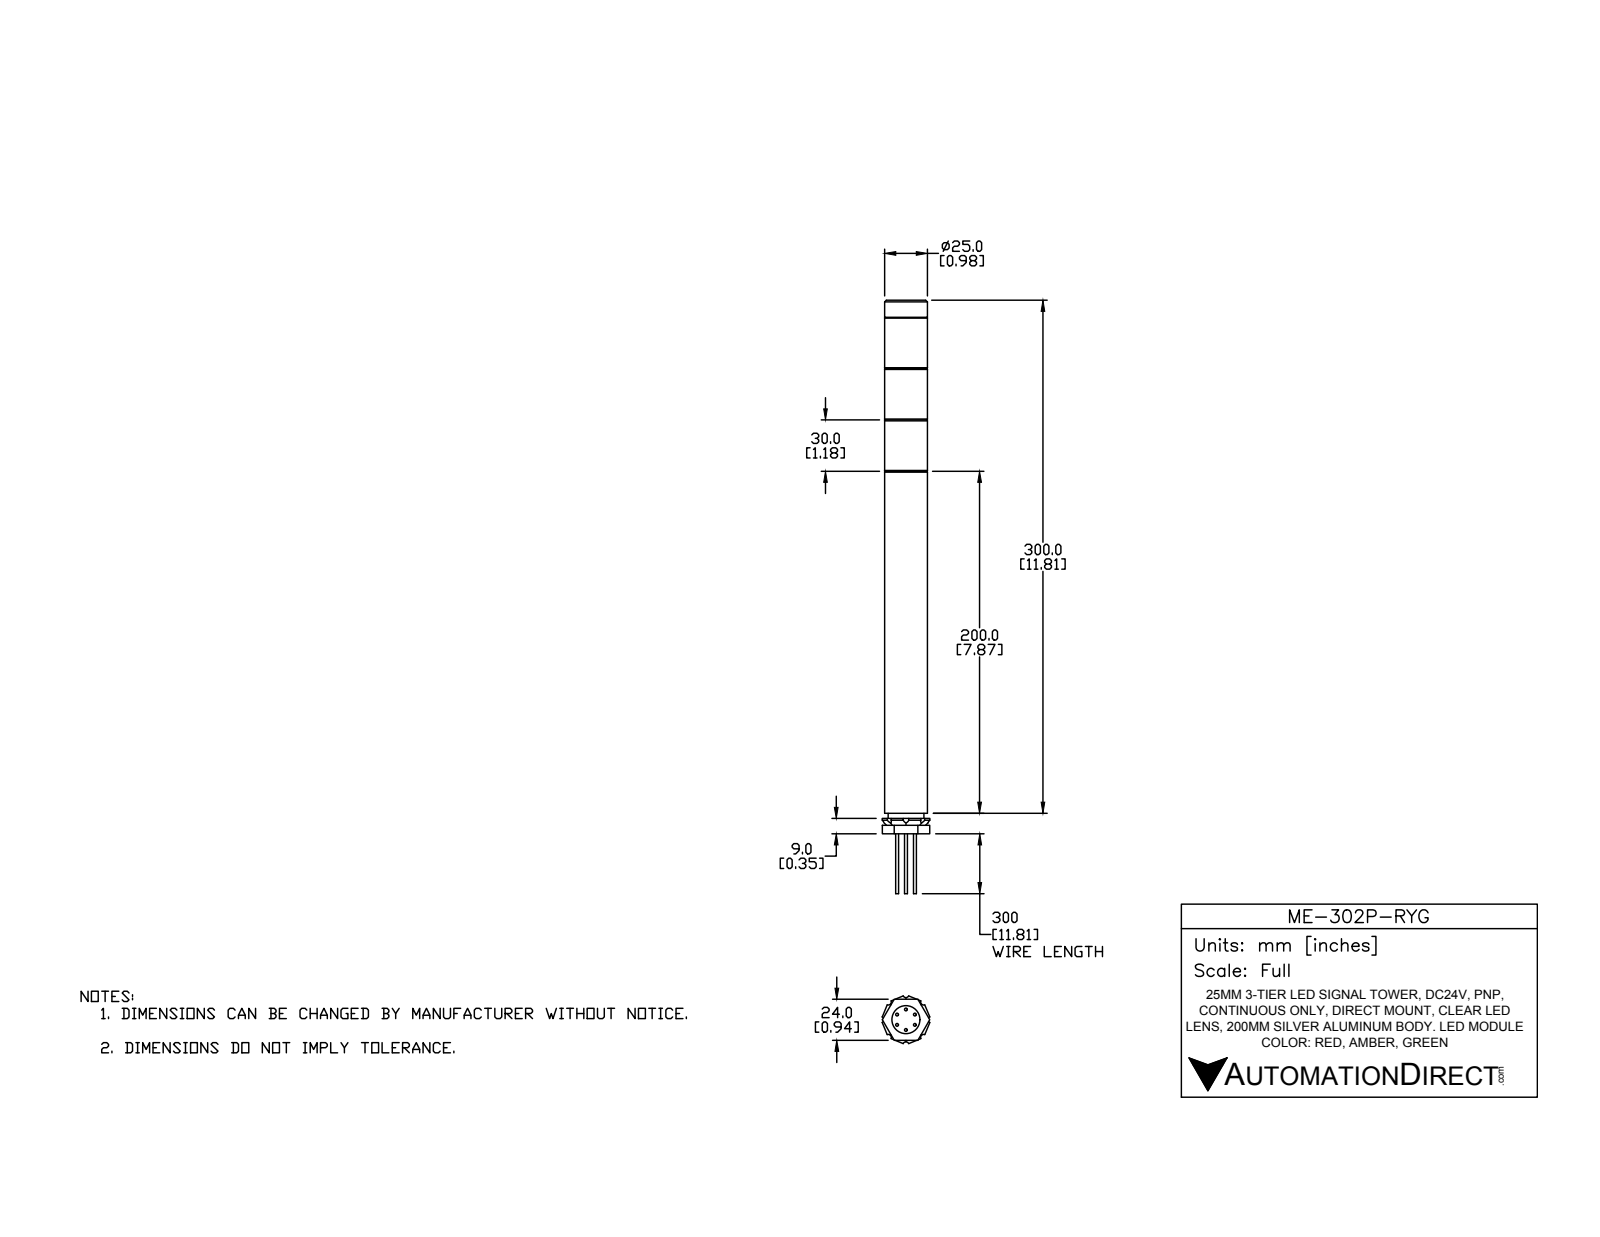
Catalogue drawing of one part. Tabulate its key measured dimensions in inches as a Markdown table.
| quantity | value |
| --- | --- |
| part name | ME-302P-RYG |
| STEP written by | SolidWorks 2016 (AUTOMOTIVE_DESIGN) |
| units | inches |
| bodies | 14 solids, 148 faces (75 planar, 51 cylindrical, 22 other) |
| overall size | 13.661 × 1.098 × 1.098 |
| volume | 8.642 in³ |
| surface area | 58.65 in² |
| round holes (diameter × count) | 0.126 × 1, 0.303 × 1, 0.646 × 1, 0.709 × 1, 0.815 × 1, 0.827 × 1 |
| round bosses / shafts (diameter × count) | 0.067 × 6, 0.984 × 1, 0.823 × 1, 0.63 × 1, 0.197 × 1 |
| partial cylindrical surfaces (radius × count) | 0.069 × 8 |
| main face-to-face distances | 1.181, 2.362, 3.543, 1.575, 10.512, 6.575, 7.756, 8.937, 10.118, 3.937 |
